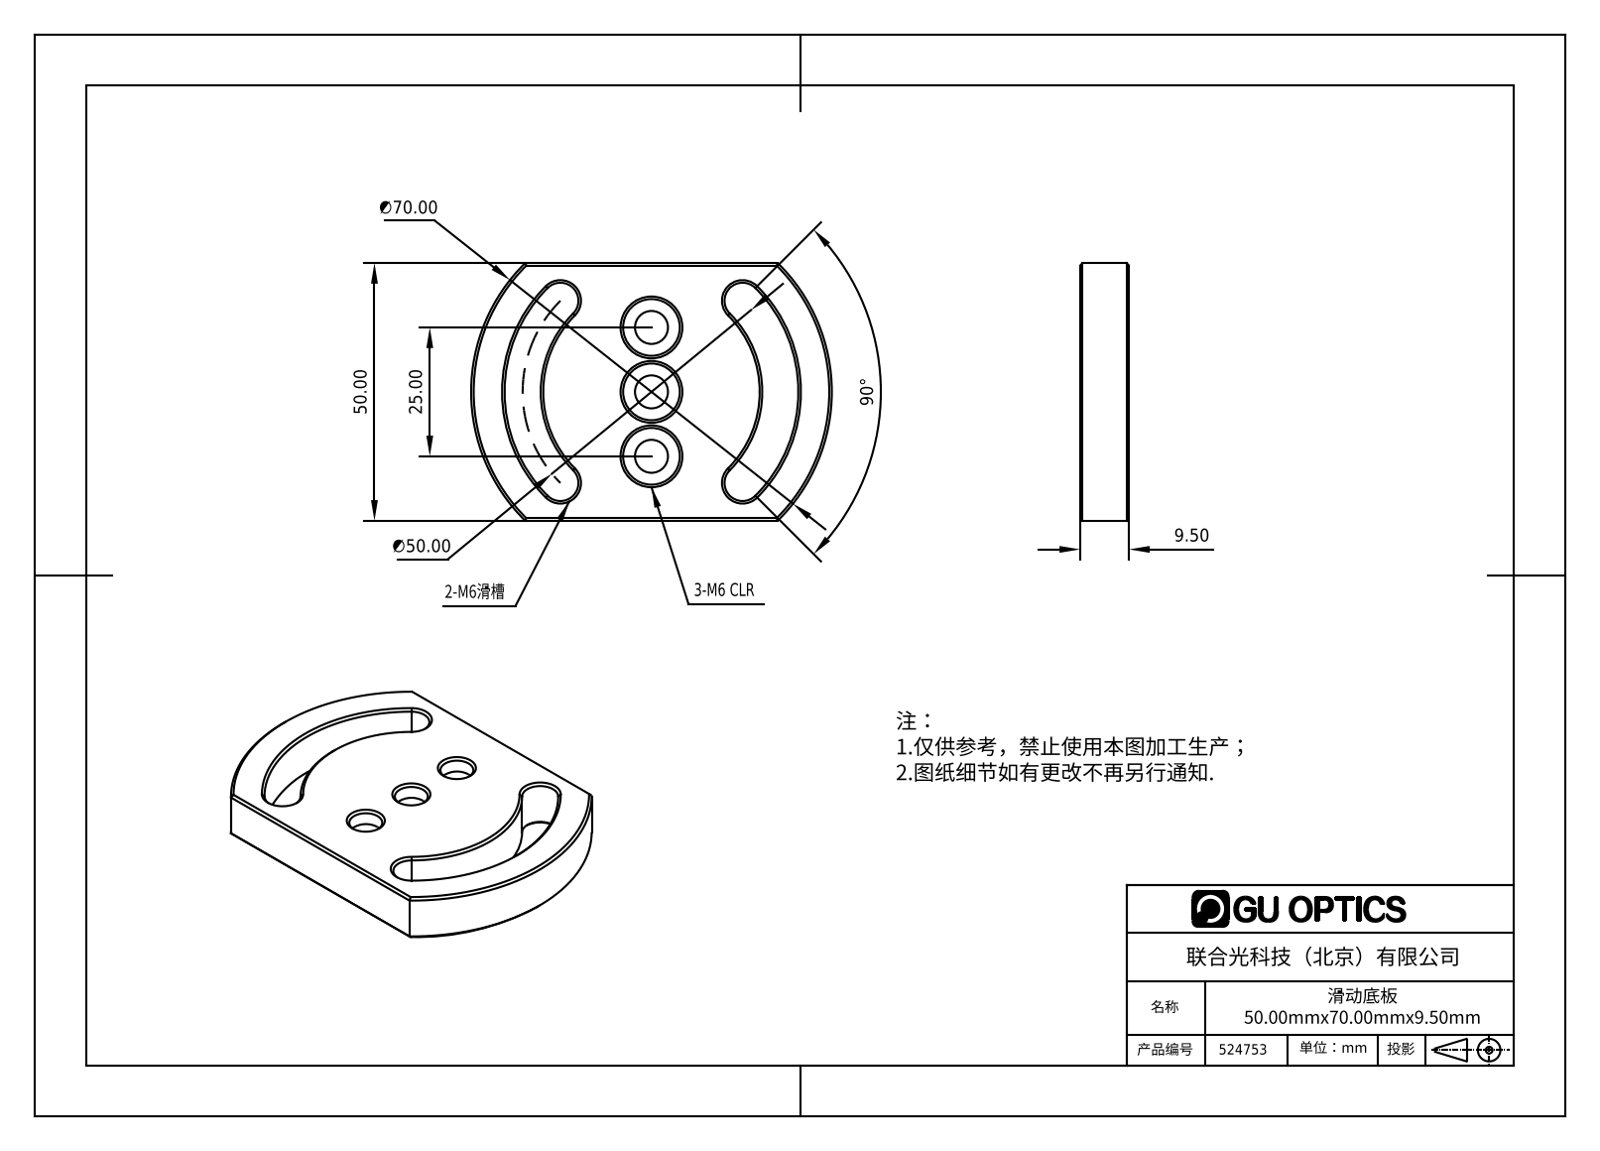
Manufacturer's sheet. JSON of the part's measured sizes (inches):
{"part_name": "SBR-2", "step_written_by": "SolidWorks 2012 (CONFIG_CONTROL_DESIGN)", "units": "inches", "bodies": {"solids": 1, "faces": 53, "planar": 11, "cylindrical": 16, "other": 26}, "overall_size": [2.756, 1.969, 0.374], "volume_in3": 1.34, "surface_area_in2": 14.52, "round_holes": [[0.252, 3], [0.433, 3]], "partial_cylinders_radius": [[0.138, 4], [0.846, 1], [1.122, 1], [1.378, 1]], "face_to_face_distances": [0.374, 1.969, 0.252, 0.122, 1.628], "hole_center_spacings": [0.492, 0.984]}
